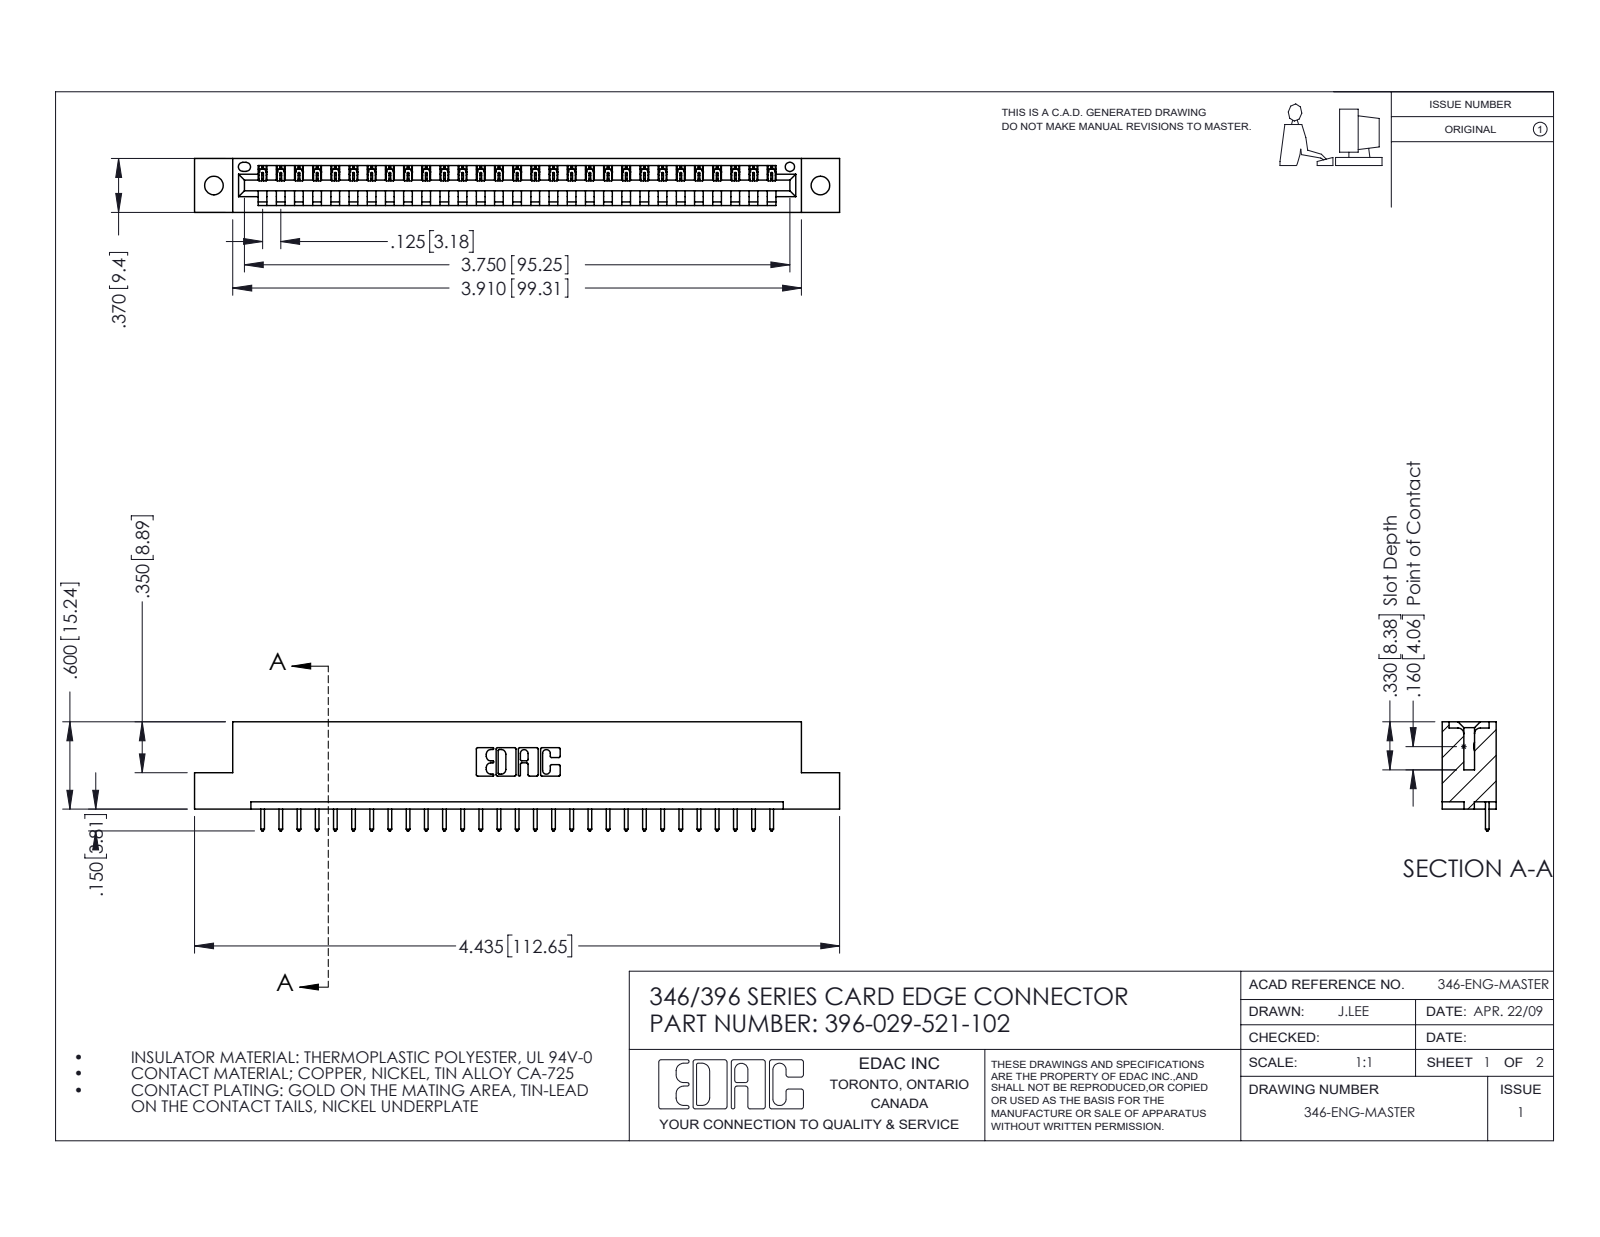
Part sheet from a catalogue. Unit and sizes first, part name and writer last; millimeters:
Units: millimetres
Overall size (bounding box): 112.6 × 19.1 × 9.4
Round holes (diameter × count): ⌀3.3 ×2, ⌀1.6 ×1
Partial cylindrical surfaces — rounded edges, fillets, slot ends (radius × count): R0.2 ×58, R0.3 ×58, R0.3 ×22, R0.2 ×6, R0.8 ×6, R0.7 ×3, R0.8 ×2, R1 ×2
Main face-to-face distances: 1.2, 8.2, 9.4, 6.4, 1.8, 7.6, 0.6, 3.8, 5.6, 2.5
Hole centre spacings: 6.2, 100.6, 105.9
Volume: 10 600 mm³ · Surface area: 12 480 mm²
Bodies: 30 solids, 1804 faces (1236 planar, 568 cylindrical, 0 other)
Part name (STEP PRODUCT): 396-029-521-102; 345-292-001_345-293-121; 346 Part_Flush Mounting Lugs - 0.128 Dia
STEP written by: SolidWorks 2016 (CONFIG_CONTROL_DESIGN)
